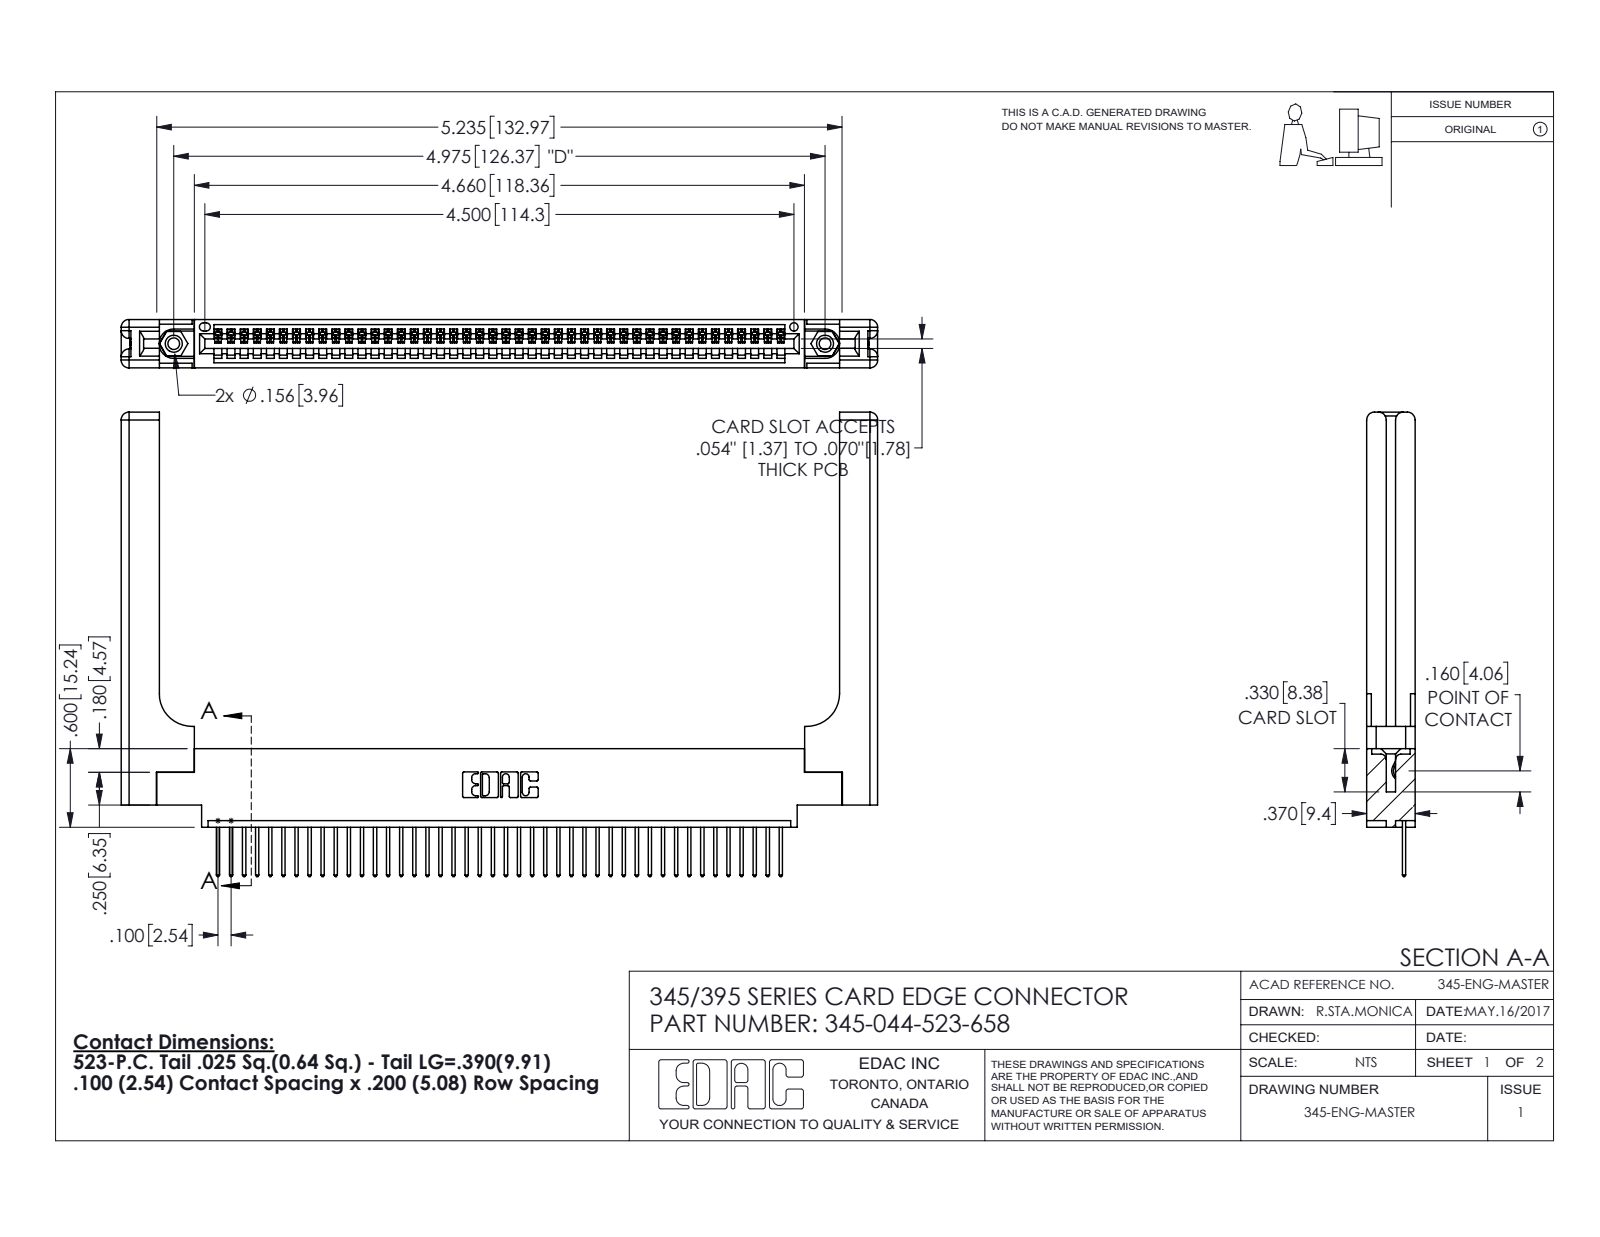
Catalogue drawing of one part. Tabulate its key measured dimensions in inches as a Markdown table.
| quantity | value |
| --- | --- |
| part name | 345-044-523-658; 345 Part_0.170 Offset - 0.156 Dia-TH; 345-292-001_345-293-123; 345-250-001_345-250-001-102 (+1 more) |
| STEP written by | SolidWorks 2016 (CONFIG_CONTROL_DESIGN) |
| units | inches |
| bodies | 49 solids, 2938 faces (1992 planar, 886 cylindrical, 60 other) |
| overall size | 5.779 × 3.547 × 0.37 |
| volume | 1.363 in³ |
| surface area | 37.02 in² |
| round holes (diameter × count) | 0.089 × 2, 0.125 × 2, 0.156 × 2, 0.064 × 1 |
| round bosses / shafts (diameter × count) | 0.155 × 2 |
| partial cylindrical surfaces (radius × count) | 0.006 × 88, 0.01 × 88, 0.01 × 22, 0.06 × 16, 0.007 × 6, 0.031 × 6, 0.026 × 3, 0.03 × 2 |
| main face-to-face distances | 0.37, 0.072, 0.298, 0.098, 0.272, 0.025, 0.2, 0.225, 0.148, 0.15 |
| hole center spacings | 0.27, 4.739, 4.975 |
